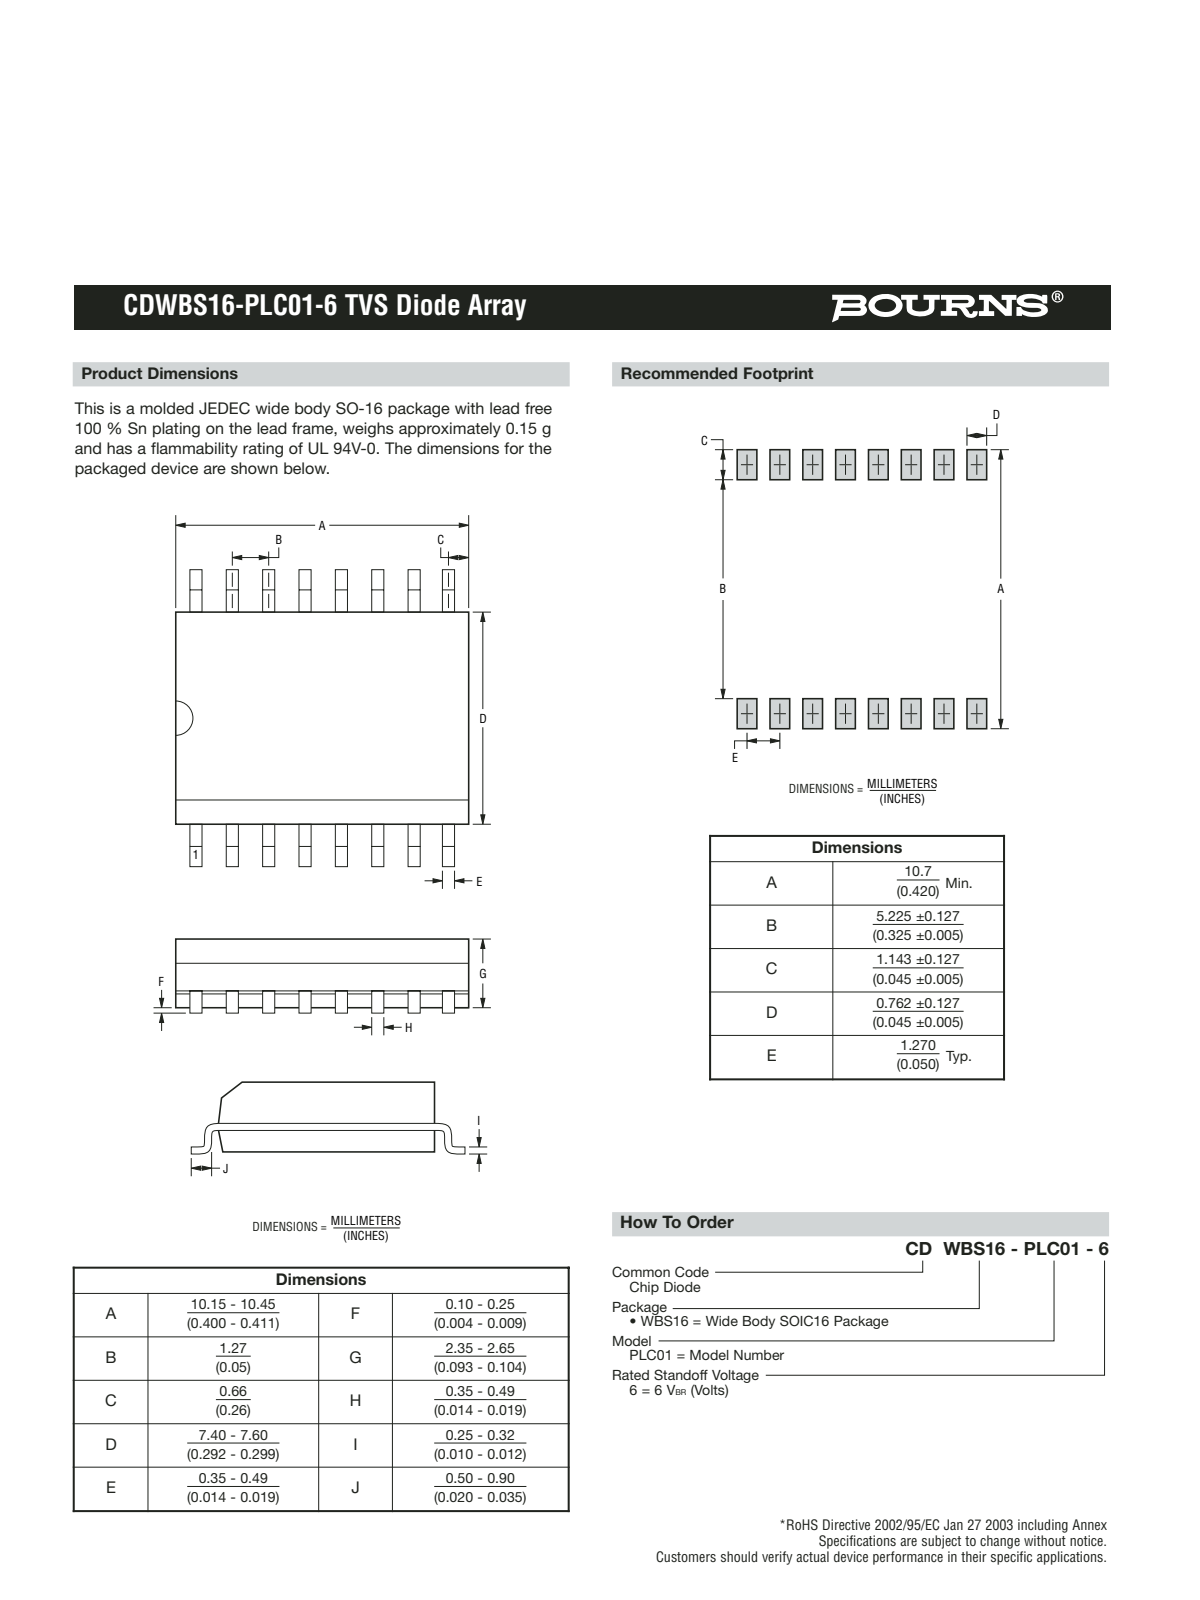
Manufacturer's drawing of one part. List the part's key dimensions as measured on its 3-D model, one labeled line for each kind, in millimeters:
Part name (STEP PRODUCT): CDWBS16-PLC01-6
STEP written by: PRO/ENGINEER BY PARAMETRIC TECHNOLOGY CORPORATION, 2010100 (CONFIG_CONTROL_DESIGN)
Units: millimetres
Bodies: 1 solid, 218 faces (153 planar, 65 cylindrical, 0 other)
Overall size (bounding box): 10.4 × 10.3 × 2.52
Volume: 182 mm³ · Surface area: 283 mm²
Partial cylindrical surfaces — rounded edges, fillets, slot ends (radius × count): R0.2 ×8, R0.38 ×1
Main face-to-face distances: 2.33, 10.31, 7.5, 1.28, 2.54, 5.08, 0.42, 0.86, 3.82, 1.26
